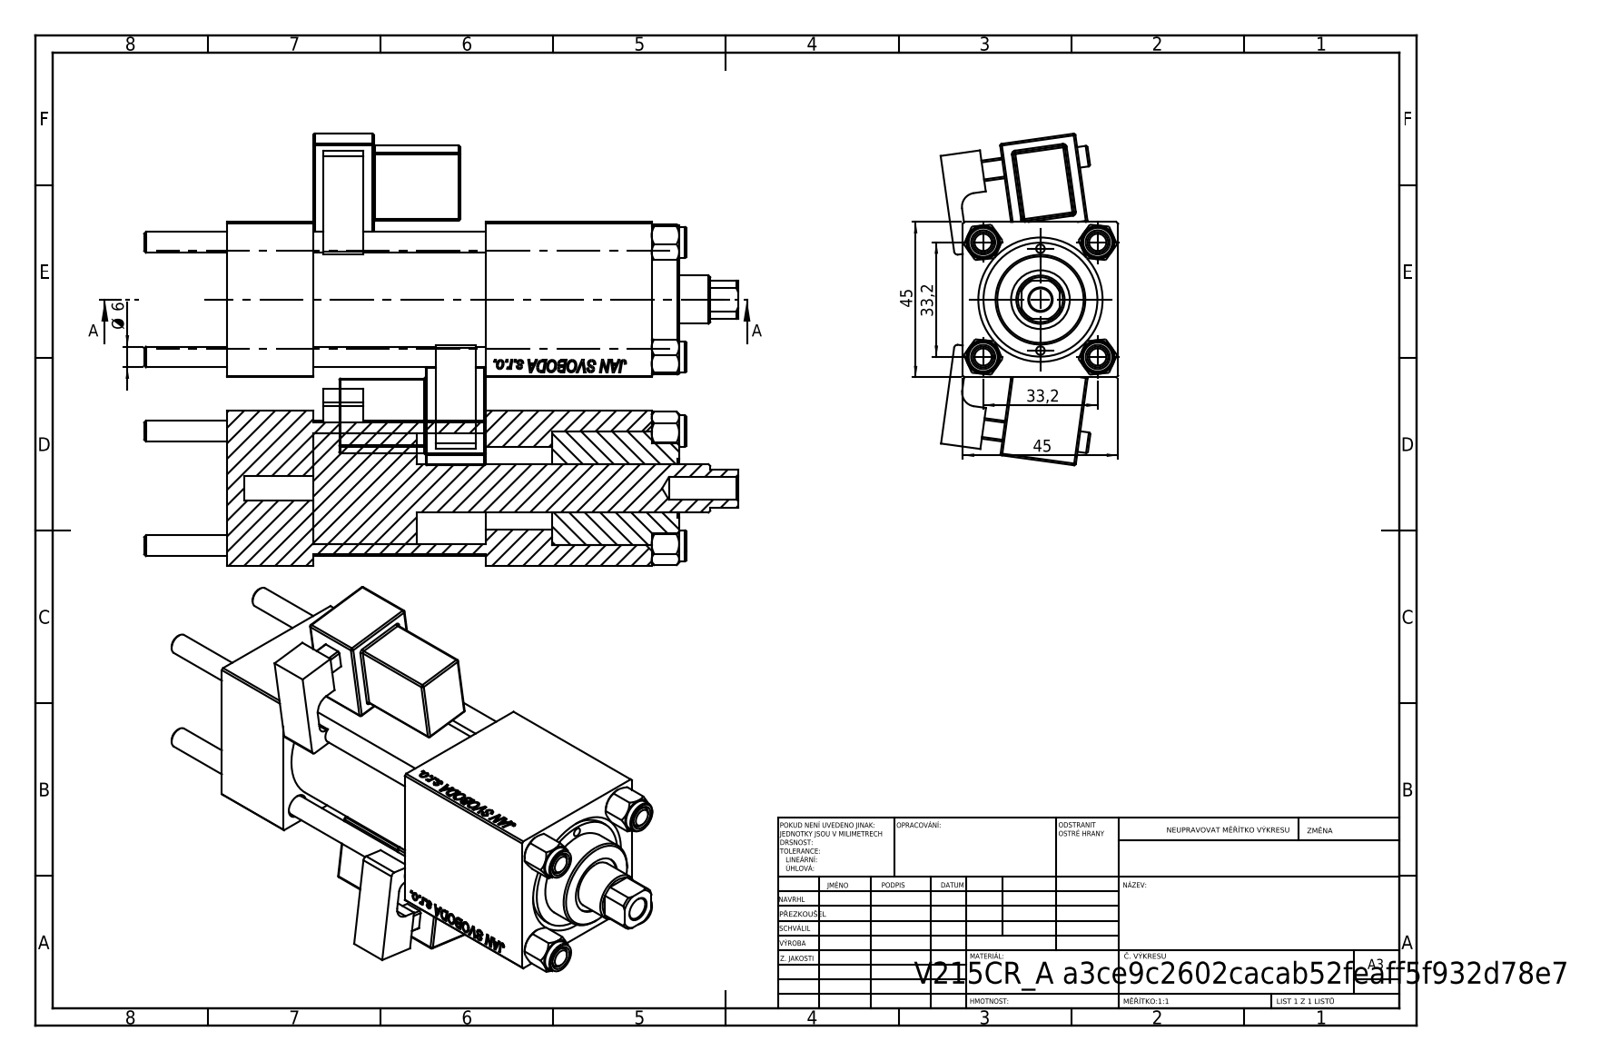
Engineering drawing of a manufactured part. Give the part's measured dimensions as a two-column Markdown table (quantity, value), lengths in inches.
| quantity | value |
| --- | --- |
| part name | V215_VC_A; NUT_M5; V215CR_MSU; V215CR_BODY_A (+2 more) |
| STEP written by | SolidWorks 2019 (CONFIG_CONTROL_DESIGN) |
| units | inches |
| bodies | 13 solids, 1297 faces (583 planar, 142 cylindrical, 572 other) |
| overall size | 6.772 × 3.781 × 2.024 |
| volume | 14.58 in³ |
| surface area | 131.6 in² |
| round holes (diameter × count) | 0.236 × 4, 0.098 × 2, 0.276 × 2, 0.518 × 2, 0.787 × 2, 0.256 × 1, 0.551 × 1, 0.669 × 1, 0.945 × 1, 1.26 × 1, 1.299 × 1 |
| round bosses / shafts (diameter × count) | 0.354 × 4, 0.236 × 2, 1.496 × 1, 1.024 × 1 |
| partial cylindrical surfaces (radius × count) | 0.02 × 48, 0.039 × 2, 0.098 × 2, 0.157 × 2, 0.256 × 1 |
| main face-to-face distances | 1.772, 0.984, 0.118, 1.969, 2.953, 3.858, 4.843, 0.591, 1.89, 1.28 |
| hole center spacings | 0.657, 0.924, 1.307, 1.396, 0.581, 1.848, 1.161, 2.972 |
